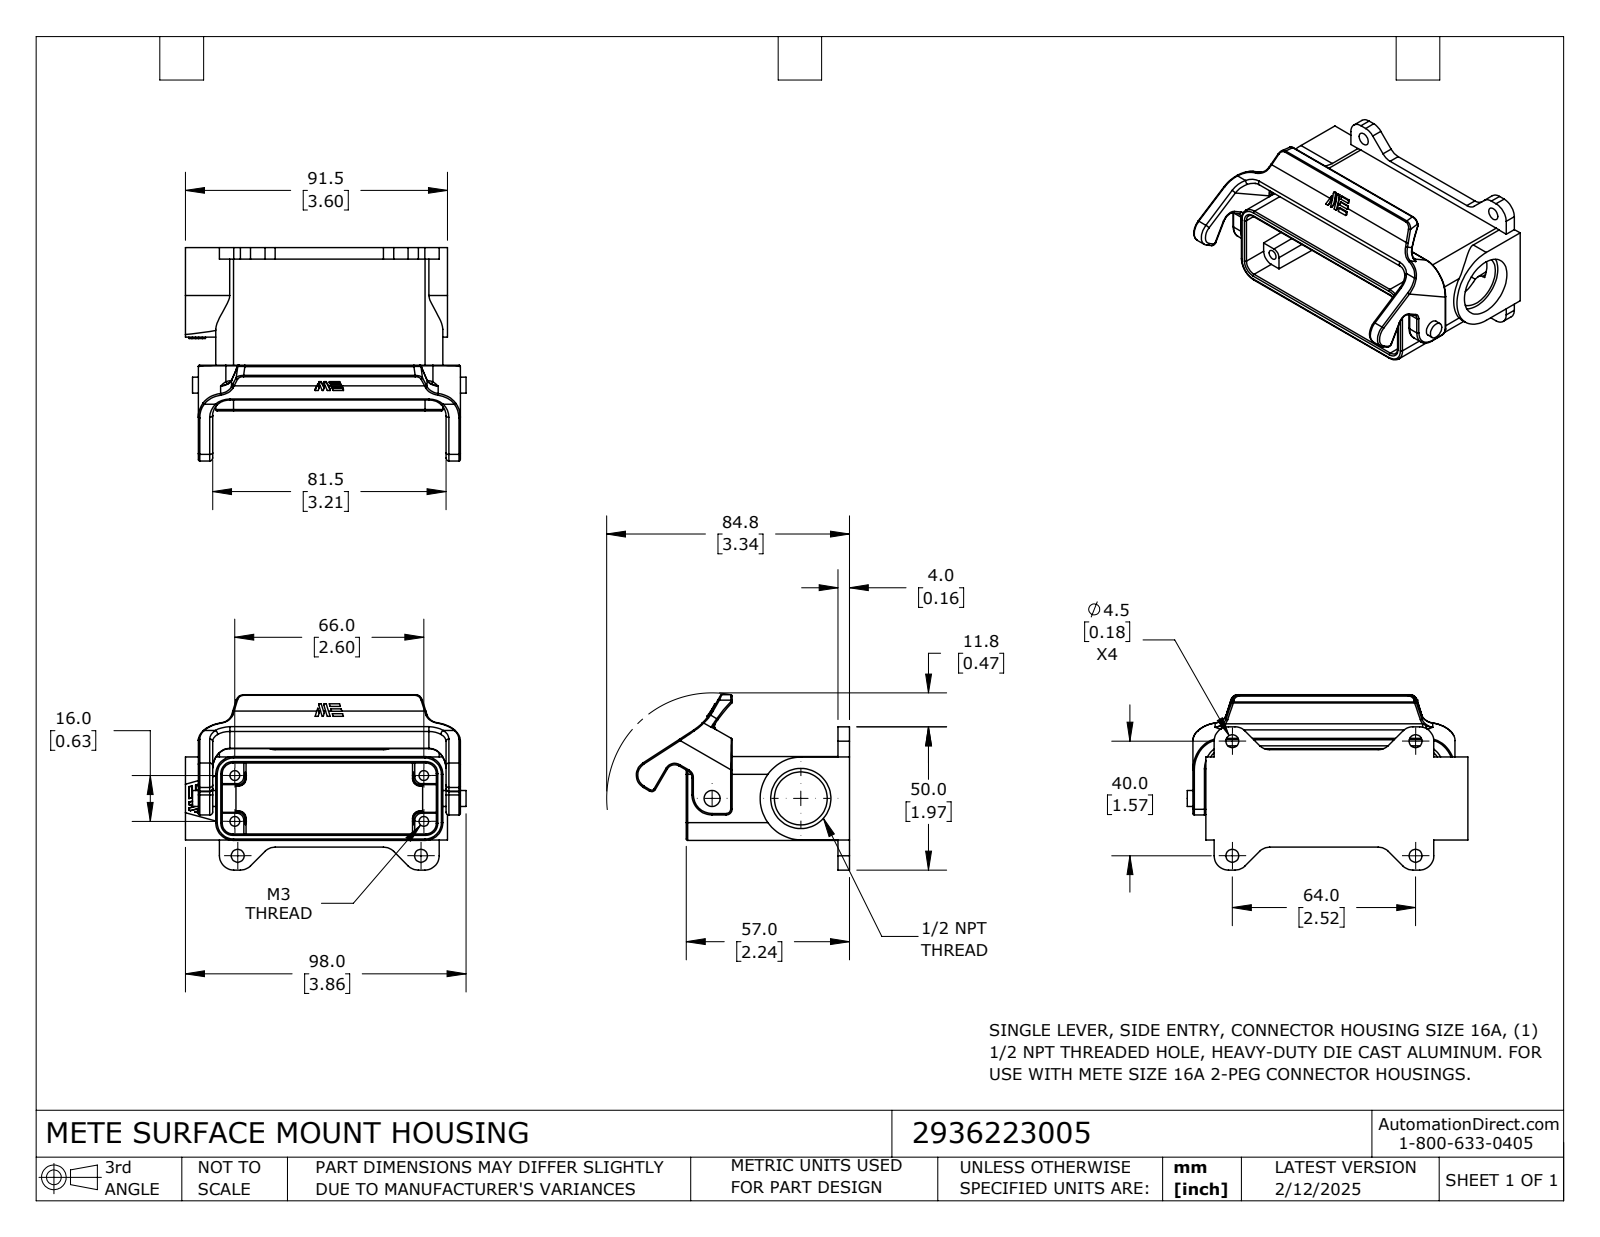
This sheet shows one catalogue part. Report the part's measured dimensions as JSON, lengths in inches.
{"part_name": "2936223005", "step_written_by": "SolidWorks 2024 (CONFIG_CONTROL_DESIGN)", "units": "inches", "bodies": {"solids": 1, "faces": 381, "planar": 148, "cylindrical": 169, "other": 64}, "overall_size": [3.858, 2.931, 2.411], "volume_in3": 3.784, "surface_area_in2": 59.21, "round_holes": [[0.134, 4], [0.177, 4], [0.728, 1], [0.827, 1]], "round_bosses_or_shafts": [[0.22, 1]], "partial_cylinders_radius": [[0.02, 30], [0.004, 19], [0.039, 16], [0.197, 15], [0.098, 7], [0.148, 4], [0.244, 4], [0.059, 2]], "face_to_face_distances": [0.089, 1.065, 1.154, 0.976, 0.157, 3.602, 0.177, 0.24, 3.362, 0.197], "hole_center_spacings": [0.474, 1.103, 2.602, 2.786, 0.63, 1.575, 2.52, 2.598]}
